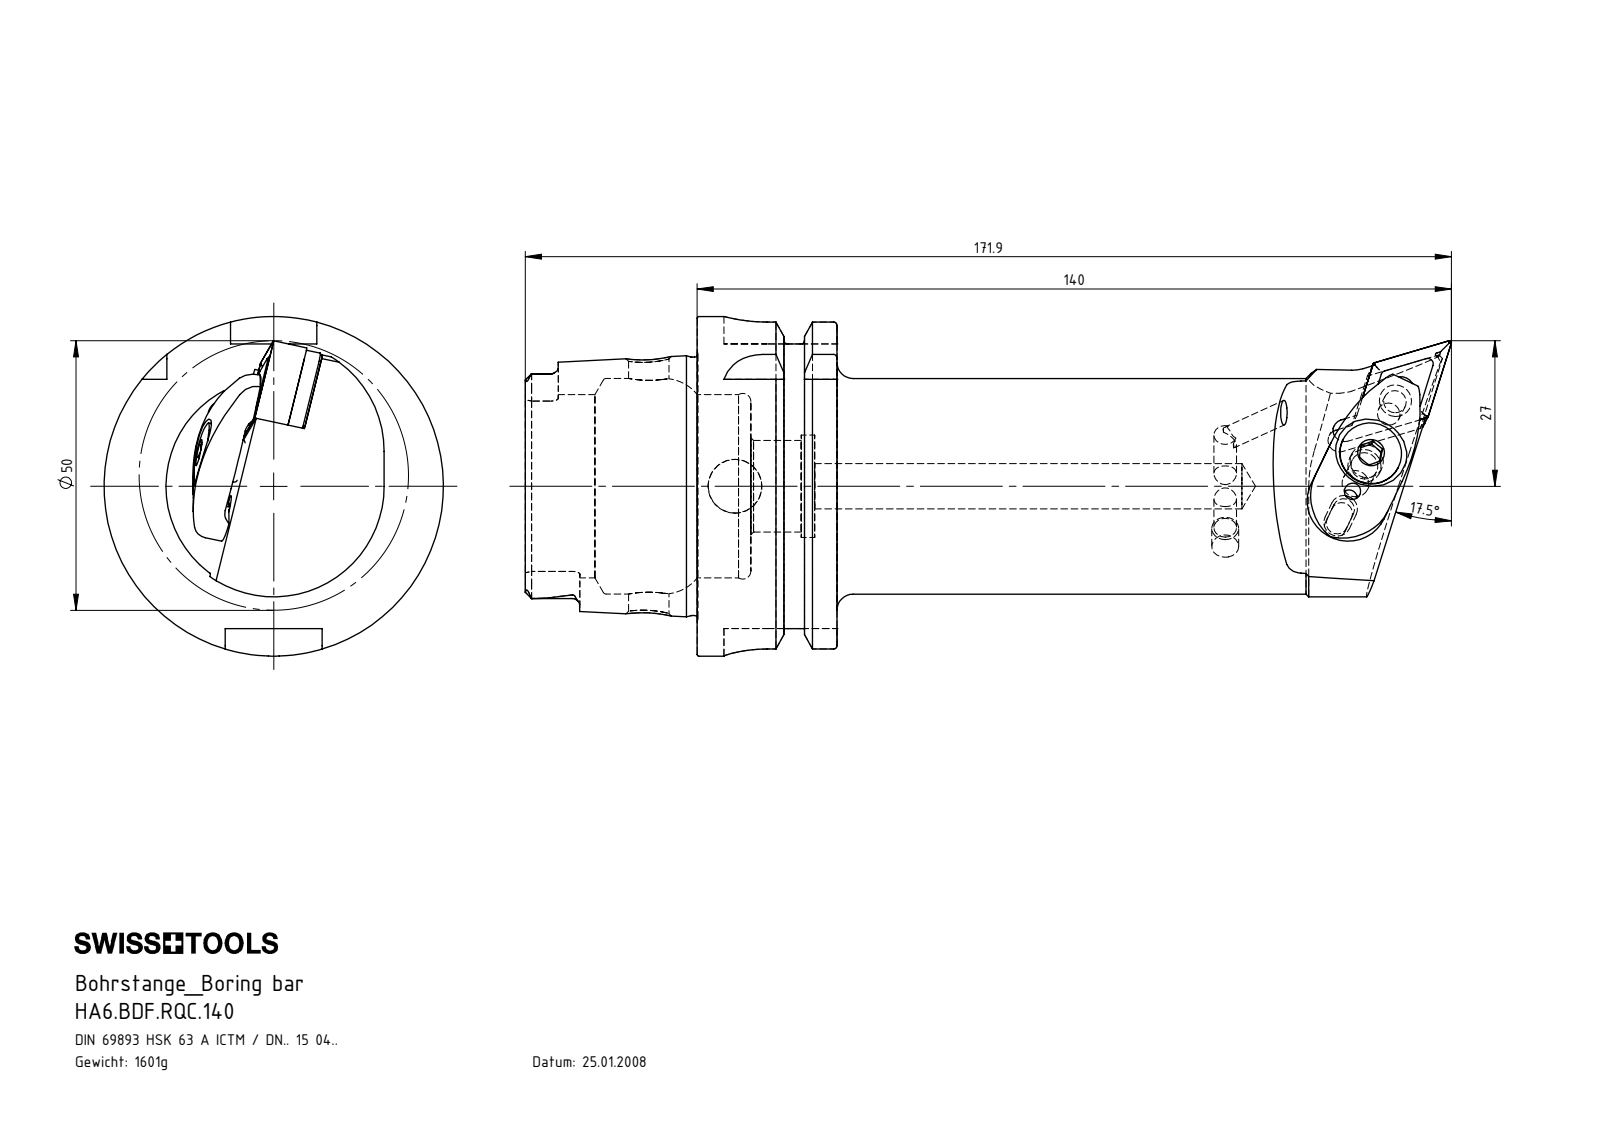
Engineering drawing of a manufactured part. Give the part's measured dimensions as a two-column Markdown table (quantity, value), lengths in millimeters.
| quantity | value |
| --- | --- |
| part name | WCC-ER4.102.020_A; WCC-ER5.102.005_A; WDF-ER2.101.003_A; DNMG150604 (+5 more) |
| STEP written by | SolidWorks 2017 (AUTOMOTIVE_DESIGN) |
| units | millimeters |
| bodies | 9 solids, 412 faces (111 planar, 133 cylindrical, 168 other) |
| overall size | 171.9 × 63 × 63 |
| volume | 204 967 mm³ |
| surface area | 42 425 mm² |
| round holes (diameter × count) | 4.2 × 3, 5 × 2, 3 × 1, 4 × 1, 5.16 × 1, 6.5 × 1, 7 × 1, 7.5 × 1, 8.4 × 1, 10 × 1, 17 × 1, 19 × 1 |
| round bosses / shafts (diameter × count) | 5 × 2, 63 × 1, 54.95 × 1, 47.94 × 1, 11.5 × 1, 7 × 1, 6.2 × 1, 6 × 1 |
| partial cylindrical surfaces (radius × count) | 0.39 × 6, 0.69 × 6, 1.4 × 6, 0.4 × 5, 8 × 4, 3 × 3, 2 × 2, 2.82 × 2 |
| main face-to-face distances | 25.95, 16, 9.95, 6.04, 31.9, 41.85, 57.85, 52.8, 21.8, 11.85 |
| hole center spacings | 14.81, 15, 23, 8, 8.19 |
